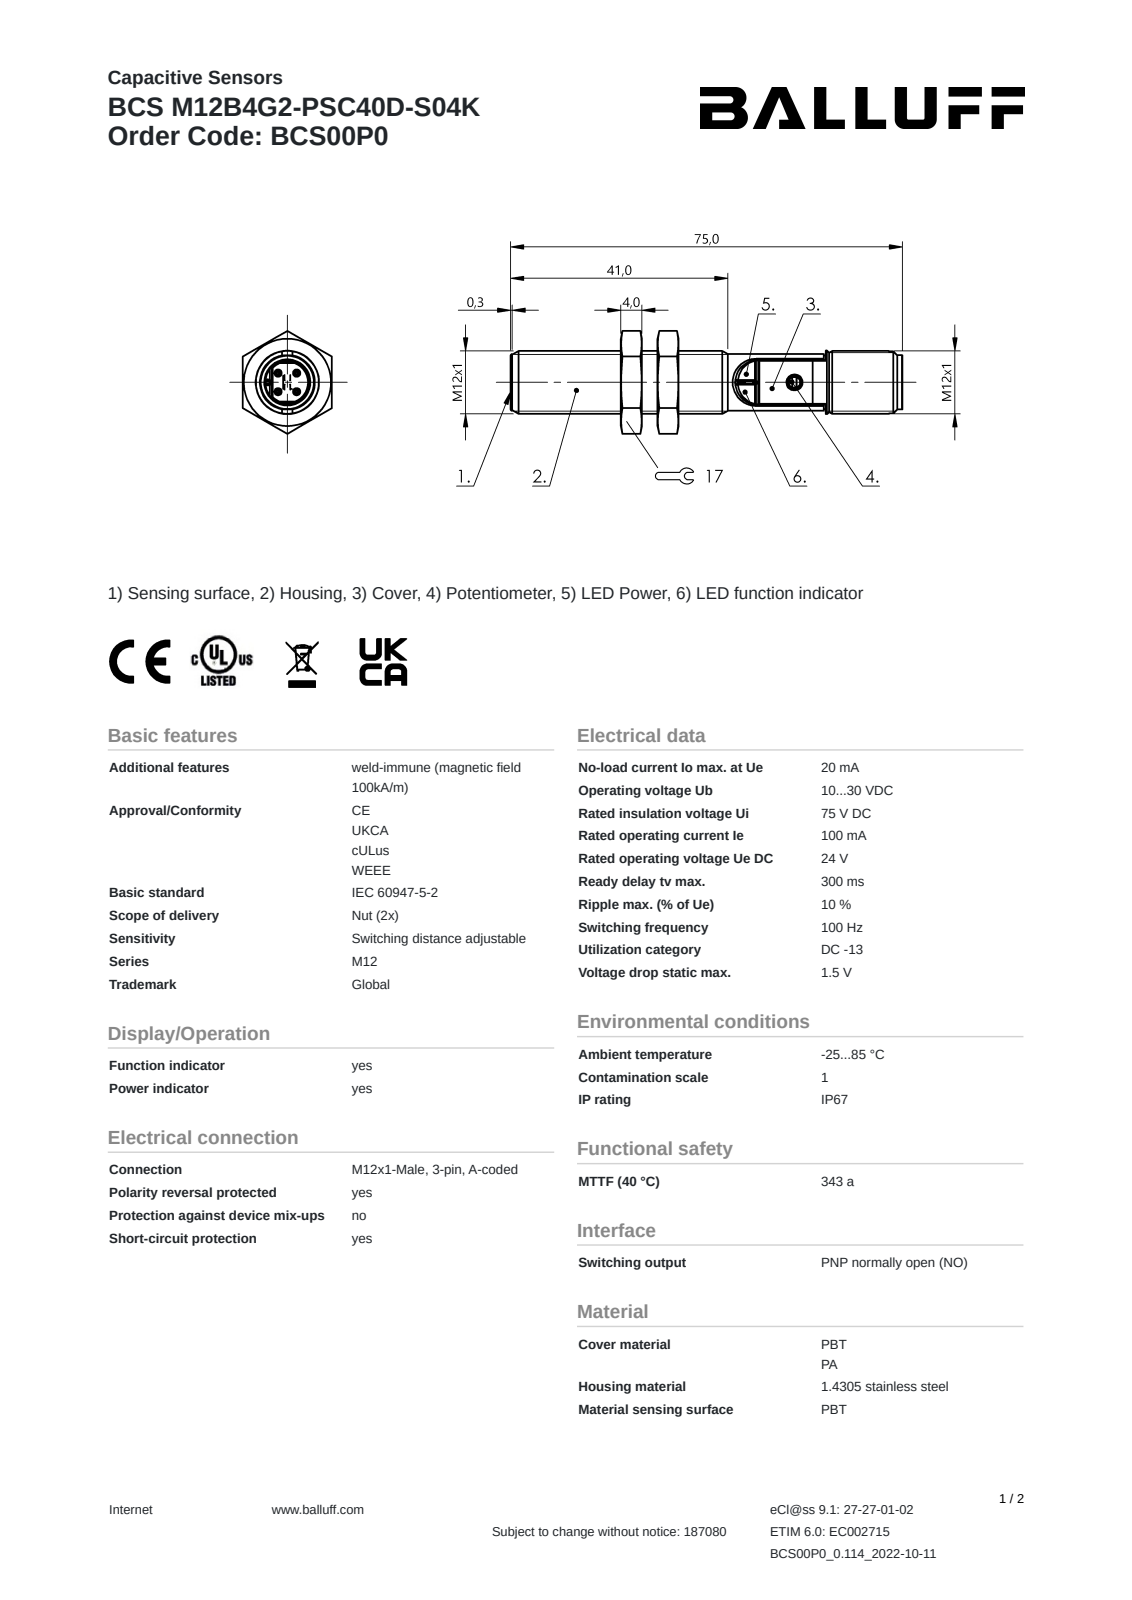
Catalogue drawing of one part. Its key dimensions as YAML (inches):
part_name: "BCS00P0"
step_written_by: "SolidWorks 2021 (AUTOMOTIVE_DESIGN)"
units: inches
bodies: {solids: 3, faces: 179, planar: 86, cylindrical: 49, other: 44}
overall_size: [2.953, 0.773, 0.669]
volume: 0.53
surface_area: 7.467
round_holes:
  - {diameter: 0.135, count: 1}
  - {diameter: 0.331, count: 1}
  - {diameter: 0.43, count: 1}
round_bosses_or_shafts:
  - {diameter: 0.039, count: 4}
  - {diameter: 0.472, count: 1}
  - {diameter: 0.467, count: 1}
  - {diameter: 0.423, count: 1}
  - {diameter: 0.407, count: 1}
  - {diameter: 0.406, count: 1}
partial_cylinders:
  - {radius: 0.004, count: 8}
  - {radius: 0.006, count: 2}
  - {radius: 0.009, count: 2}
  - {radius: 0.01, count: 1}
  - {radius: 0.024, count: 1}
  - {radius: 0.061, count: 1}
  - {radius: 0.156, count: 1}
  - {radius: 0.157, count: 1}
face_to_face_distances: [0.276, 0.157, 0.669, 0.433, 0.118, 0.413, 0.846, 0.689, 0.571, 1.76]
